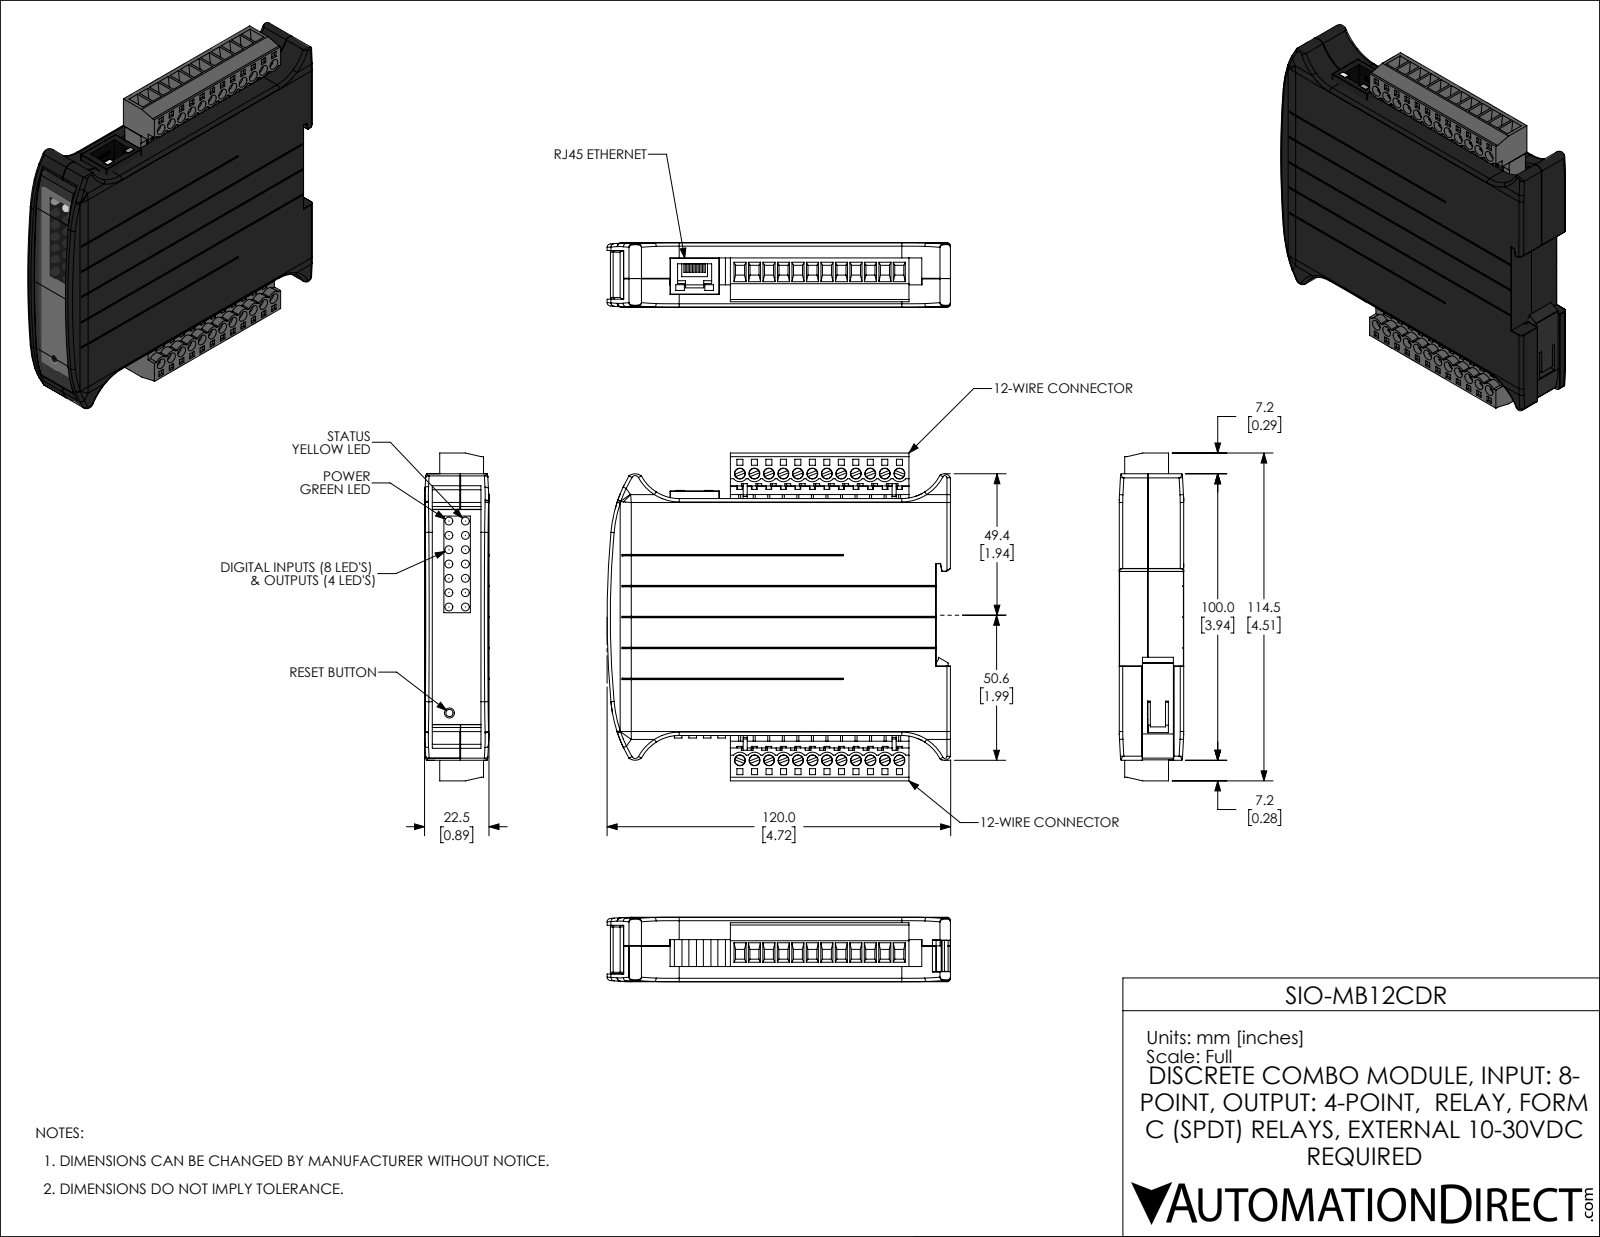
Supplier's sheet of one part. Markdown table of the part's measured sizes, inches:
| quantity | value |
| --- | --- |
| part name | SIO-MB12CDR |
| STEP written by | SolidWorks 2019 (AUTOMOTIVE_DESIGN) |
| units | inches |
| bodies | 14 solids, 3468 faces (2687 planar, 518 cylindrical, 263 other) |
| overall size | 4.72 × 4.506 × 0.886 |
| volume | 5.264 in³ |
| surface area | 143.8 in² |
| round holes (diameter × count) | 0.15 × 24, 0.094 × 2, 0.138 × 1 |
| round bosses / shafts (diameter × count) | 0.142 × 24, 0.079 × 24, 0.108 × 14, 0.154 × 1, 0.098 × 1, 0.091 × 1 |
| partial cylindrical surfaces (radius × count) | 0.004 × 128, 0.112 × 48, 0.113 × 24, 0.01 × 20, 0.047 × 12, 1.988 × 9, 0.005 × 8, 0.008 × 6 |
| main face-to-face distances | 0.059, 0.827, 0.886, 0.768, 0.028, 0.618, 0.209, 0.15, 0.283, 0.677 |
| hole center spacings | 0.199, 0.398, 0.598, 0.797, 3.946, 0.996, 3.941, 1.195 |
